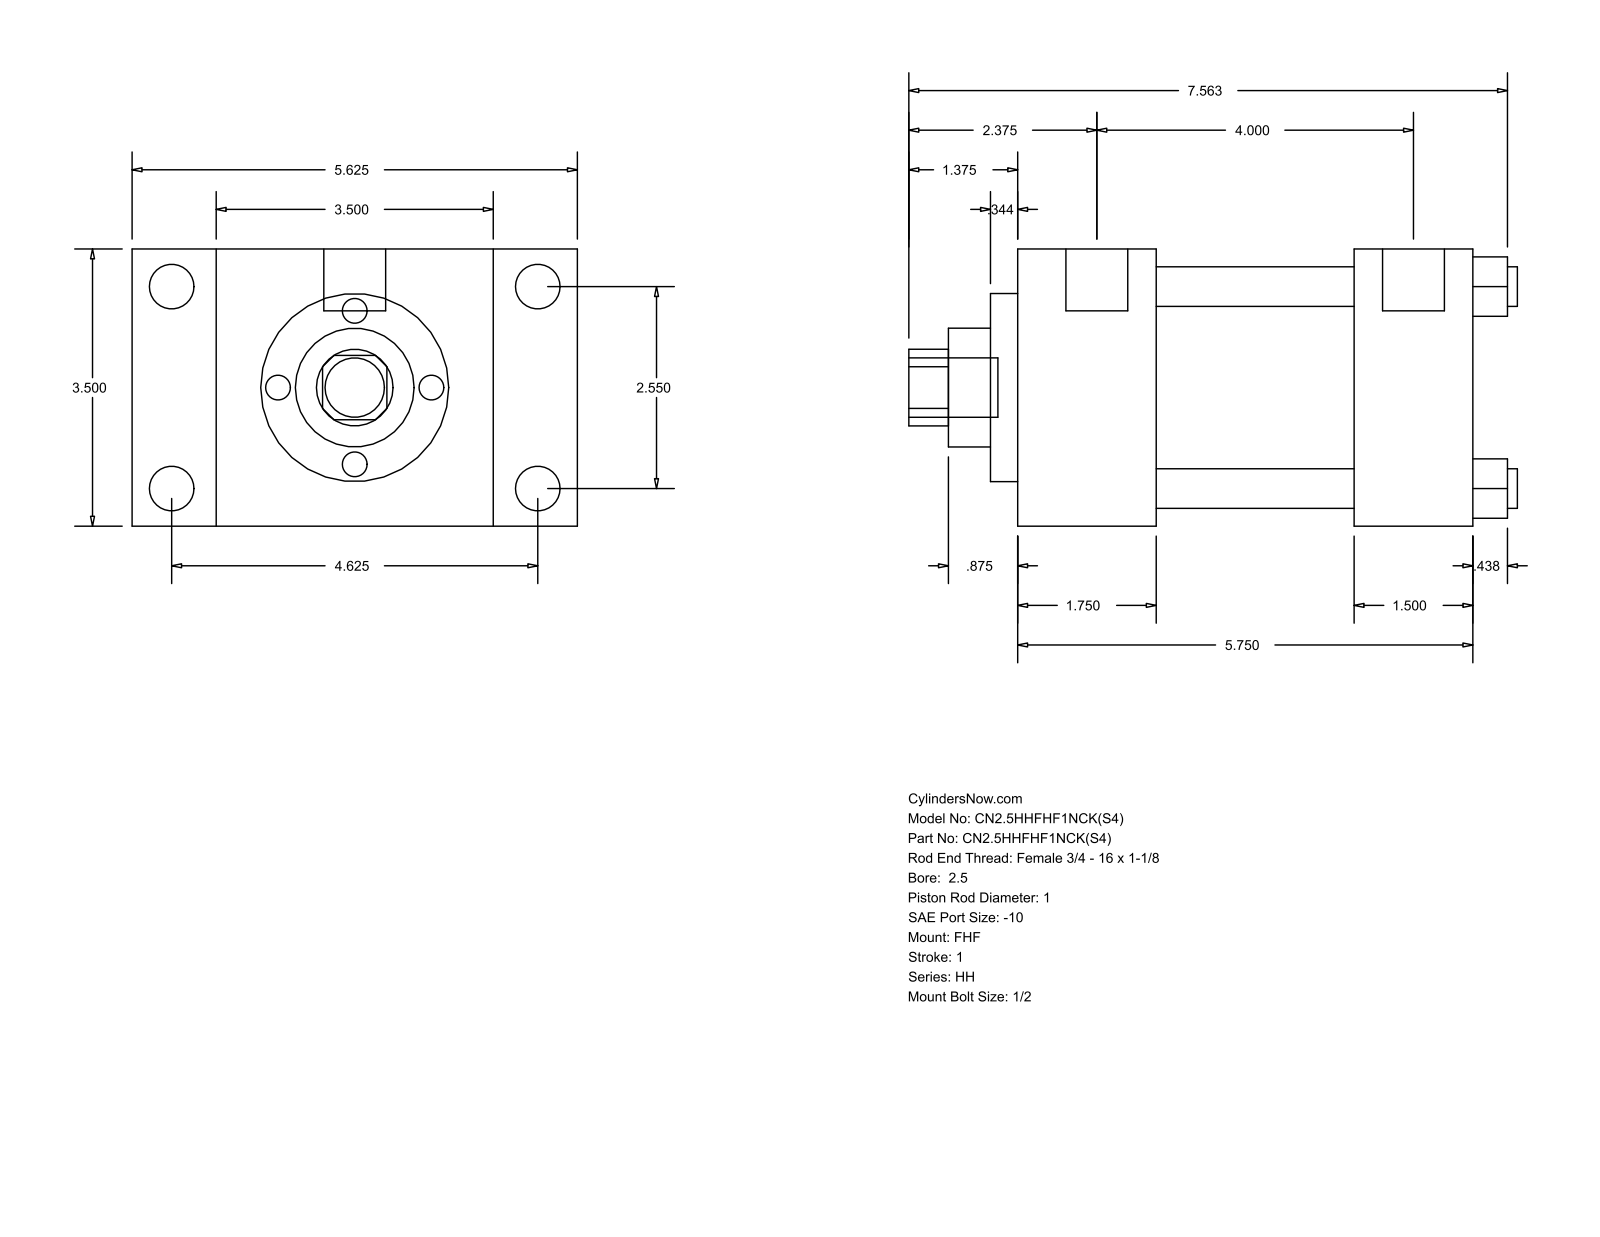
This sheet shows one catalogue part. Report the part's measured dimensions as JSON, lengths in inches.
{"part_name": "HH_FHF__0250_1", "step_written_by": "GSSL Pune (CONFIG_CONTROL_DESIGN)", "units": "inches", "bodies": {"solids": 0, "faces": 90, "planar": 61, "cylindrical": 29, "other": 0}, "overall_size": [7.687, 5.625, 3.5], "round_holes": [[0.5, 4], [1, 1], [1.5, 1], [2.375, 1], [2.875, 1]], "round_bosses_or_shafts": [[0.563, 4], [0.219, 4], [0.781, 2], [0.75, 1]], "partial_cylinders_radius": [[0.484, 1]], "face_to_face_distances": [3.5, 1.75, 1.063, 4.563, 5.75, 4, 5.625, 4.25, 2.5, 1.5], "hole_center_spacings": [1.803, 2.55, 3.606]}
